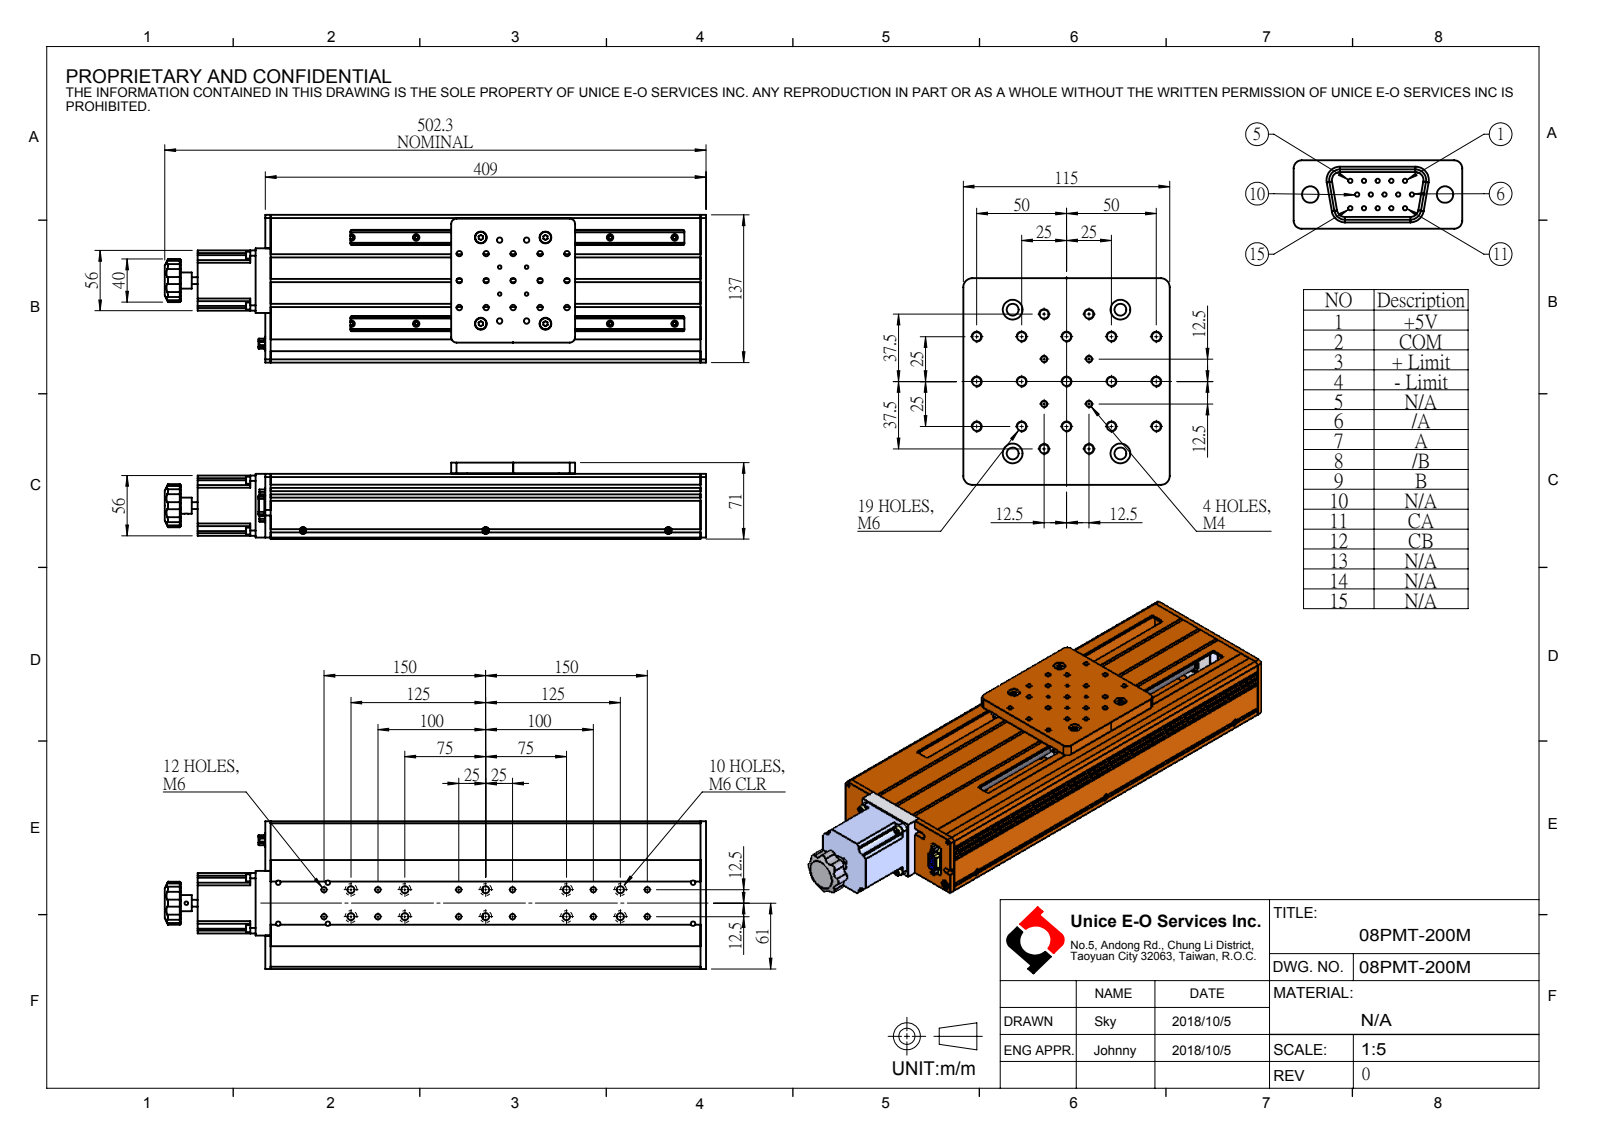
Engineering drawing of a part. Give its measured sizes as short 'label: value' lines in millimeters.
name: 08PMT-200M
written by: SolidWorks 2016 (AUTOMOTIVE_DESIGN)
unit: mm
bodies: 0 solids, 789 faces (372 planar, 300 cylindrical, 117 other)
size: 502.3 × 137 × 71
holes: 31× ⌀5, 14× ⌀11, 11× ⌀0.8, 10× ⌀6.6, 6× ⌀1, 6× ⌀3.3, 6× ⌀4.2, 2× ⌀2, 2× ⌀2.5, 1× ⌀18, 1× ⌀22, 1× ⌀26
bosses: 4× ⌀6.5, 3× ⌀5.8, 2× ⌀7.7, 2× ⌀3, 1× ⌀16, 1× ⌀15, 1× ⌀6.35
rounds: 12× R1.5, 8× R4, 8× R5, 8× R7.41, 7× R0.5, 4× R2, 4× R4.5, 3× R3
face distances: 60.5, 2, 135, 133, 10.5, 1.5, 59, 137, 1.7, 9
hole spacings: 25, 35.36, 50, 55.9, 125, 75, 79.06, 100
